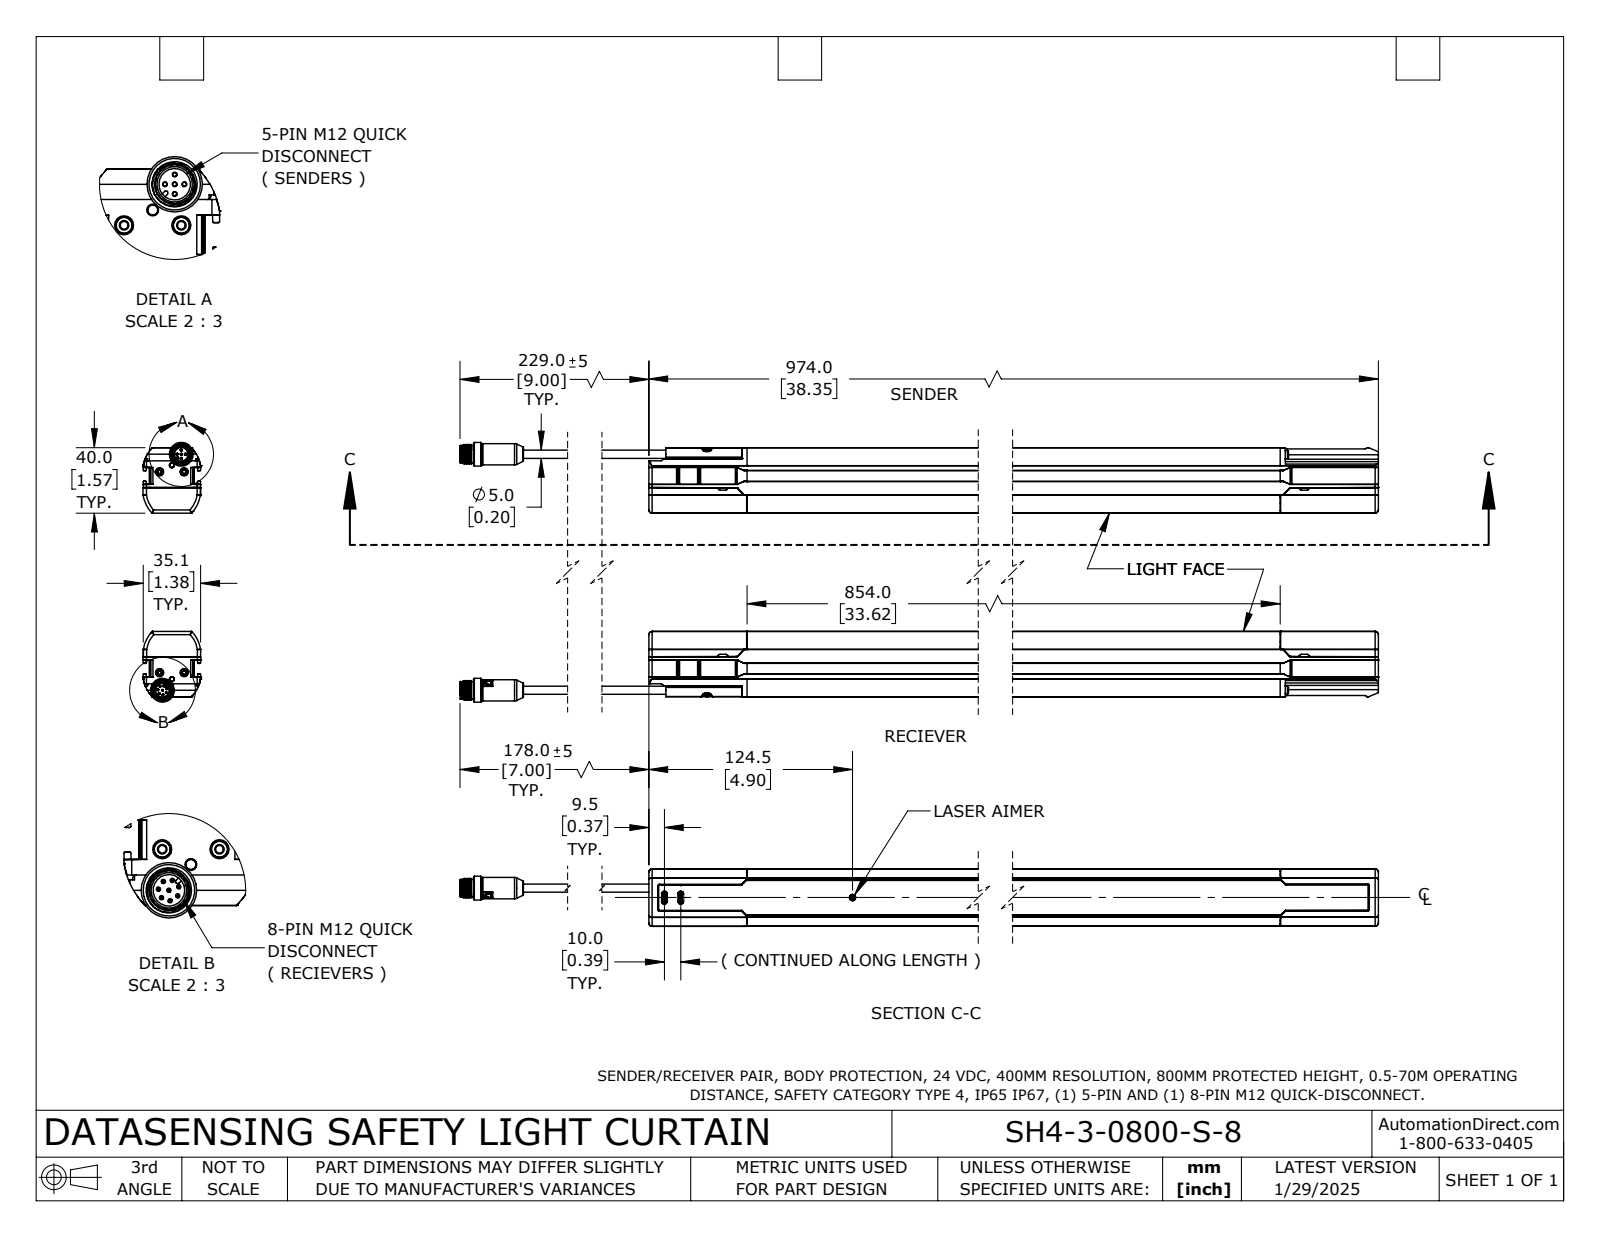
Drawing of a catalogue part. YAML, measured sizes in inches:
part_name: "SH4-3-0800-S-8"
step_written_by: "SolidWorks 2024 (AUTOMOTIVE_DESIGN)"
units: inches
bodies: {solids: 4, faces: 2640, planar: 1204, cylindrical: 784, other: 652}
overall_size: [47.335, 6.248, 1.384]
volume: 139.8
surface_area: 627.4
round_holes:
  - {diameter: 0.079, count: 4}
  - {diameter: 0.118, count: 4}
  - {diameter: 0.197, count: 4}
  - {diameter: 0.079, count: 2}
  - {diameter: 0.325, count: 2}
  - {diameter: 0.382, count: 2}
  - {diameter: 0.407, count: 2}
  - {diameter: 0.425, count: 2}
  - {diameter: 0.11, count: 1}
  - {diameter: 0.138, count: 1}
round_bosses_or_shafts:
  - {diameter: 0.197, count: 10}
  - {diameter: 0.087, count: 8}
  - {diameter: 0.031, count: 8}
  - {diameter: 0.039, count: 5}
  - {diameter: 0.172, count: 4}
  - {diameter: 0.571, count: 2}
  - {diameter: 0.512, count: 2}
  - {diameter: 0.417, count: 2}
partial_cylinders:
  - {radius: 0.01, count: 164}
  - {radius: 0.016, count: 66}
  - {radius: 0.02, count: 50}
  - {radius: 0.008, count: 36}
  - {radius: 0.031, count: 20}
  - {radius: 0.031, count: 12}
  - {radius: 0.079, count: 12}
  - {radius: 0.059, count: 10}
face_to_face_distances: [1.496, 4.496, 0.156, 1.222, 3, 1.378, 5.992, 1.067, 1.033, 4.634]
hole_center_spacings: [0.429, 0.591, 0.672, 4.831, 4.867, 5.254, 5.28, 5.695]
